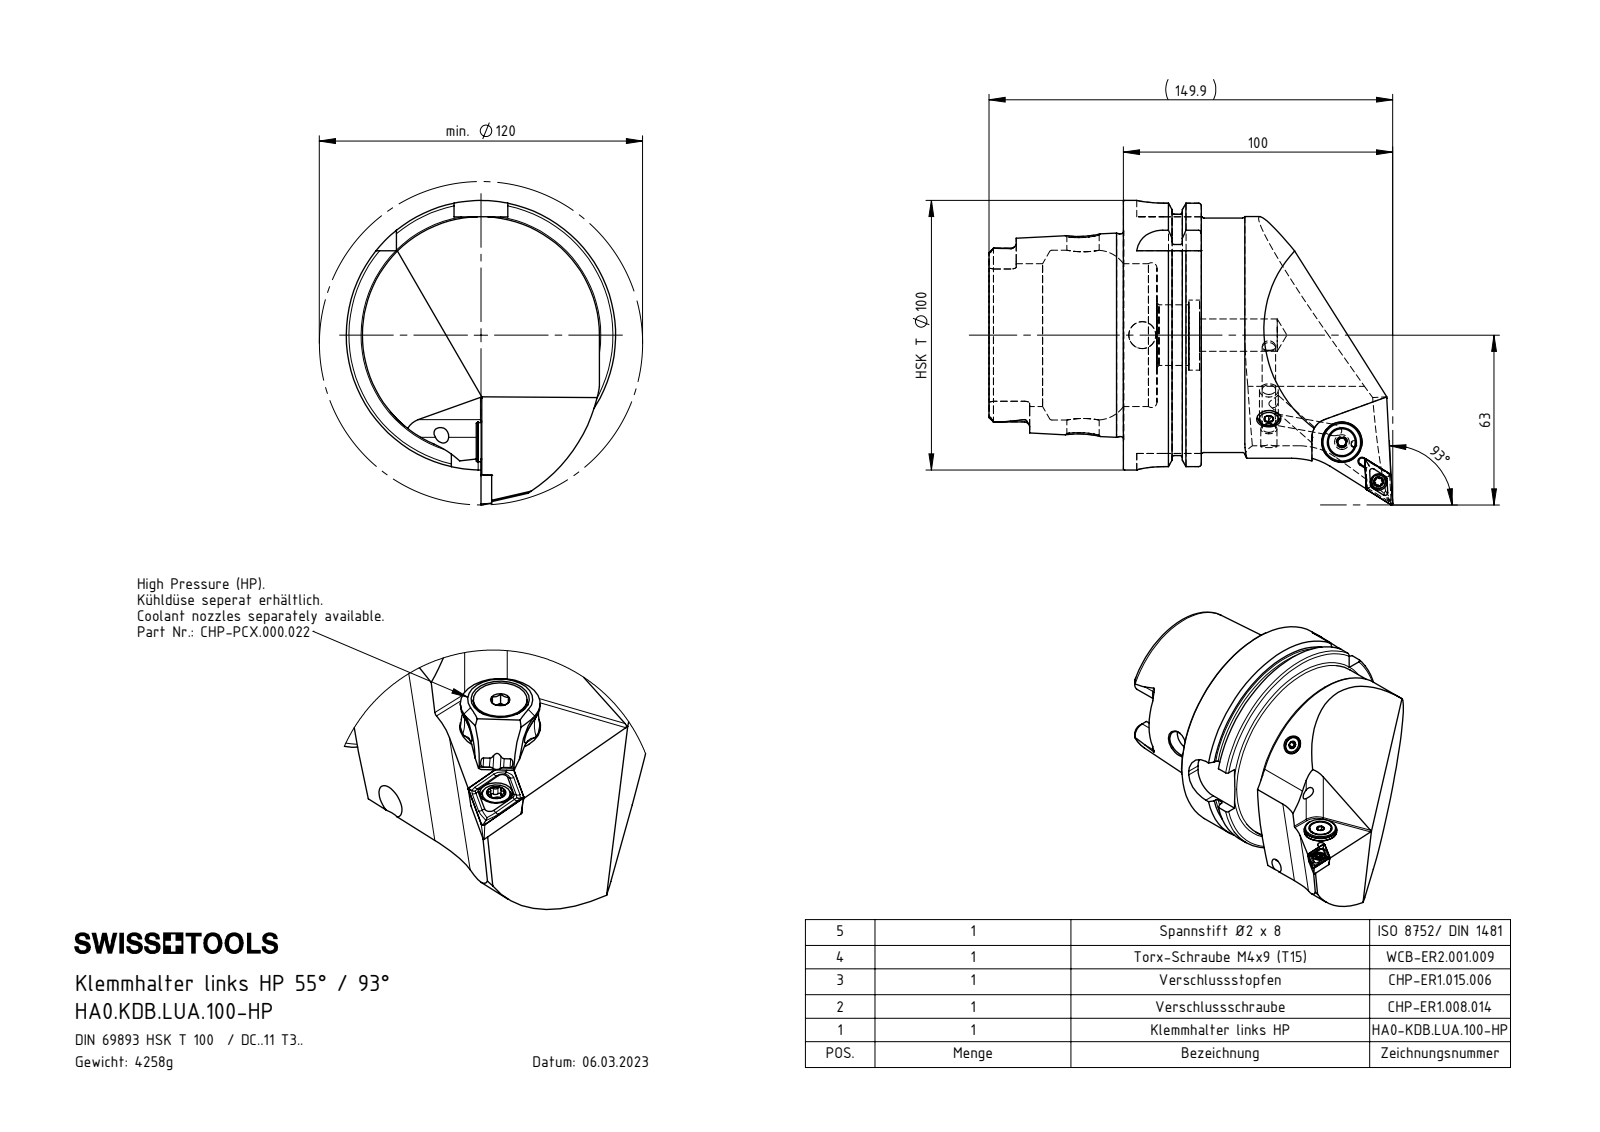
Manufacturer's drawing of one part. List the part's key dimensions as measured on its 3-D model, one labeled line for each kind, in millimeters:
Part name (STEP PRODUCT): DIN 3771 - 13x1; HA0.KDB.LUA.100-HP; ISO 8752 2x8; WCB-ER2.001.009_A (+7 more)
STEP written by: SolidWorks 2017 (AUTOMOTIVE_DESIGN)
Units: millimetres
Bodies: 10 solids, 449 faces (116 planar, 131 cylindrical, 202 other)
Overall size (bounding box): 149.9 × 113.01 × 100
Volume: 542 492 mm³ · Surface area: 70 727 mm²
Round holes (diameter × count): ⌀5 ×4, ⌀4.2 ×2, ⌀12 ×2, ⌀1.2 ×1, ⌀2 ×1, ⌀2.5 ×1, ⌀3 ×1, ⌀3.3 ×1, ⌀4.4 ×1, ⌀5.2 ×1, ⌀6 ×1, ⌀6.1 ×1
Round bosses / shafts (diameter × count): ⌀100 ×1, ⌀91.95 ×1, ⌀87 ×1, ⌀75.26 ×1, ⌀15 ×1, ⌀13.4 ×1, ⌀10 ×1, ⌀8 ×1
Partial cylindrical surfaces — rounded edges, fillets, slot ends (radius × count): R0.34 ×6, R0.59 ×6, R1.9 ×6, R10 ×4, R0.5 ×2, R4.83 ×2, R4.88 ×2, R1.25 ×1
Main face-to-face distances: 12.45, 28.95, 16.5, 49.9, 62.35, 78.85, 87.8, 43.7, 78.2, 28.3
Hole centre spacings: 4.49, 16.71, 16.83, 20.01, 20.13, 84.08, 88.33, 103.21
